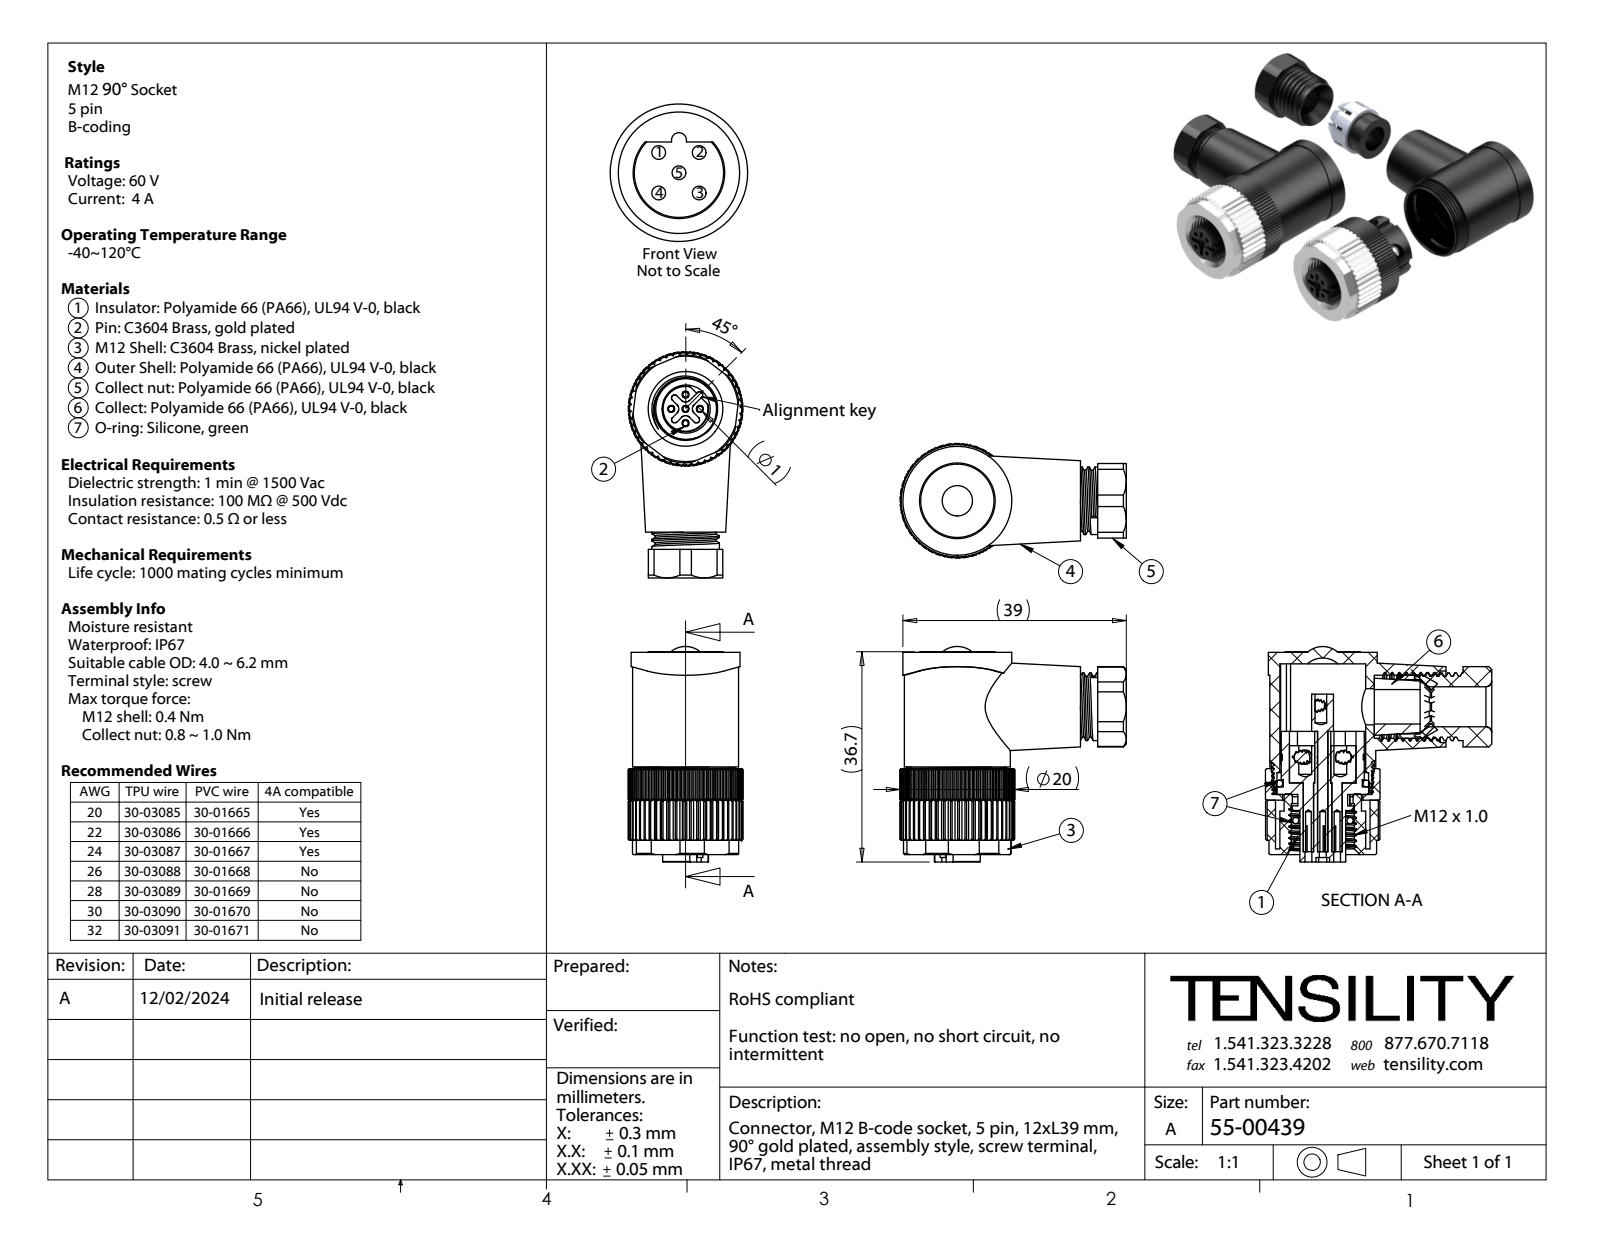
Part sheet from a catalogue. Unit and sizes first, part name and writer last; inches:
Units: inches
Overall size (bounding box): 1.555 × 1.48 × 0.787
Round holes (diameter × count): ⌀0.098 ×9, ⌀0.039 ×5, ⌀0.047 ×5, ⌀0.081 ×5, ⌀0.071 ×4, ⌀0.197 ×4, ⌀0.433 ×2, ⌀0.236 ×1, ⌀0.248 ×1, ⌀0.276 ×1, ⌀0.374 ×1, ⌀0.417 ×1
Round bosses / shafts (diameter × count): ⌀0.138 ×5, ⌀0.094 ×5, ⌀0.748 ×1, ⌀0.728 ×1, ⌀0.701 ×1, ⌀0.67 ×1, ⌀0.669 ×1, ⌀0.571 ×1
Partial cylindrical surfaces — rounded edges, fillets, slot ends (radius × count): R0.069 ×5, R0.022 ×4, R0.039 ×4, R0.254 ×1, R0.256 ×1, R0.276 ×1, R0.37 ×1, R0.394 ×1
Main face-to-face distances: 0.039, 0.079, 0.898, 0.976, 1.016, 0.374, 0.465, 0.492, 0.529, 0.543
Hole centre spacings: 0.202, 0.202, 0.031, 0.098, 0.123, 0.139, 0.143, 0.171
Volume: 0.542 in³ · Surface area: 22.09 in²
Bodies: 18 solids, 1522 faces (545 planar, 518 cylindrical, 459 other)
Part name (STEP PRODUCT): 55-00439-06; 55-00439-10; 55-00439-09; 55-00439_revA (+8 more)
STEP written by: SolidWorks 2021 (CONFIG_CONTROL_DESIGN)
